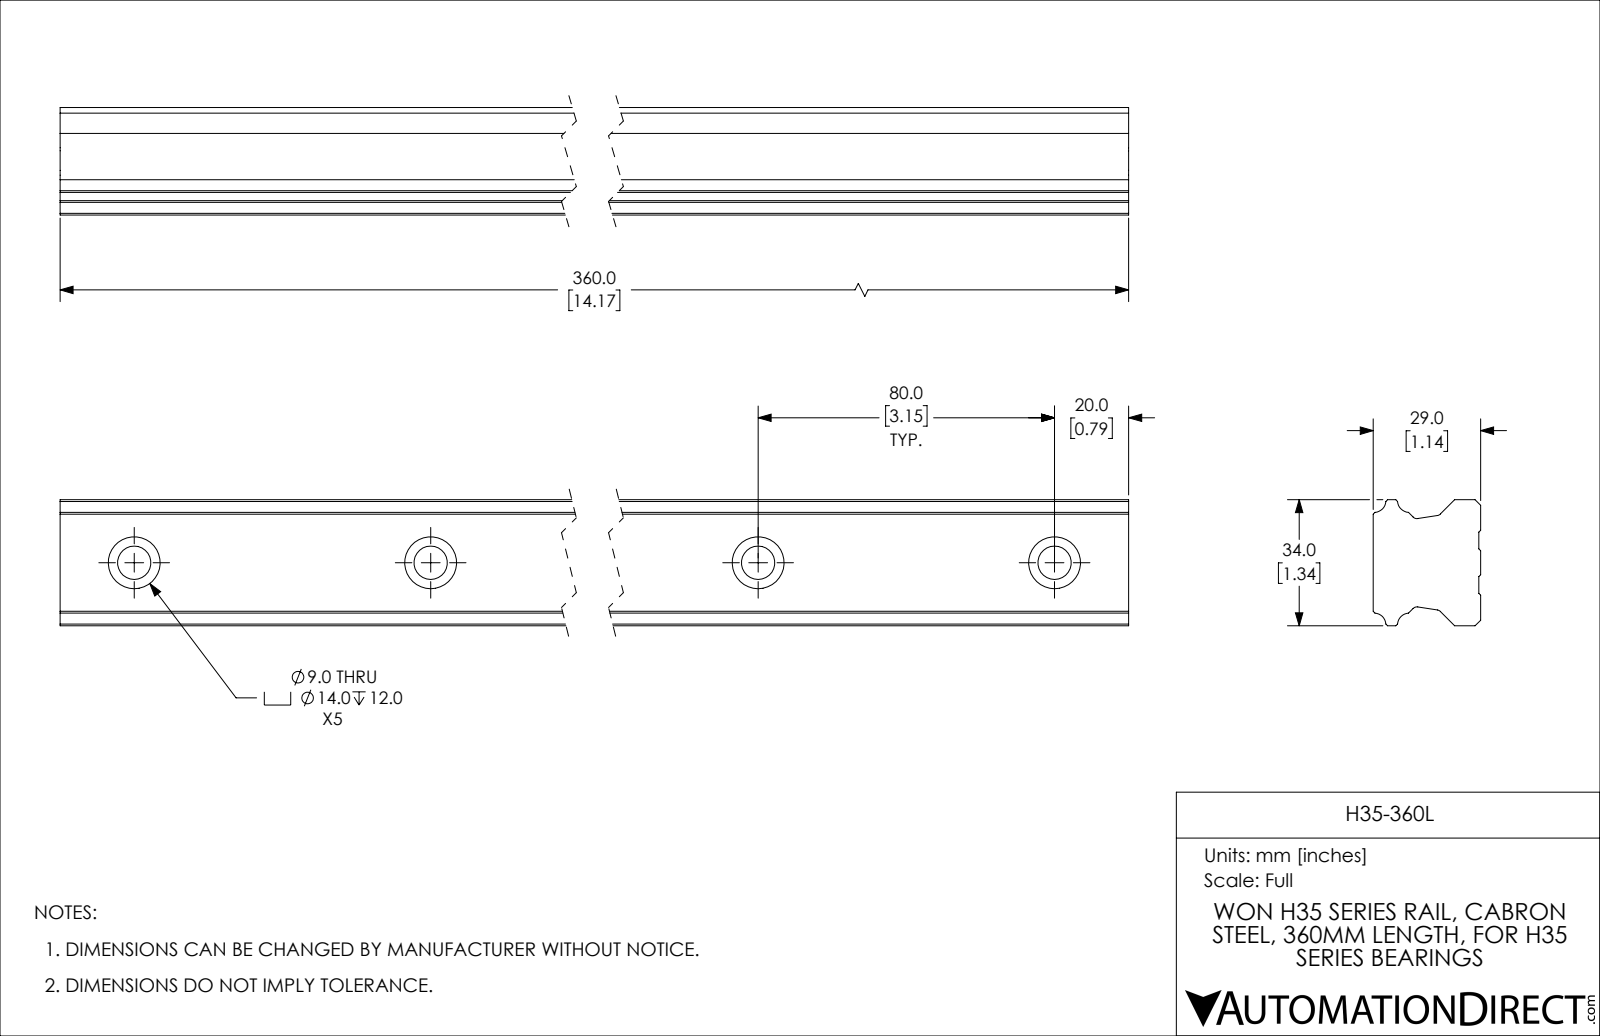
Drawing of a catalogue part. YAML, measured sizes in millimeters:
part_name: "H35-360L"
step_written_by: "SolidWorks 2019 (CONFIG_CONTROL_DESIGN)"
units: millimeters
bodies: {solids: 1, faces: 78, planar: 50, cylindrical: 28, other: 0}
overall_size: [360, 34, 29]
volume: 291082
surface_area: 52730
round_holes:
  - {diameter: 9, count: 5}
  - {diameter: 14, count: 5}
partial_cylinders:
  - {radius: 1.5, count: 4}
  - {radius: 3.2, count: 4}
face_to_face_distances: [29, 0.5, 28.5, 34, 12.8, 15.13, 27.93, 40.72, 25.59, 12.79]
hole_center_spacings: [80, 160, 240, 320]
